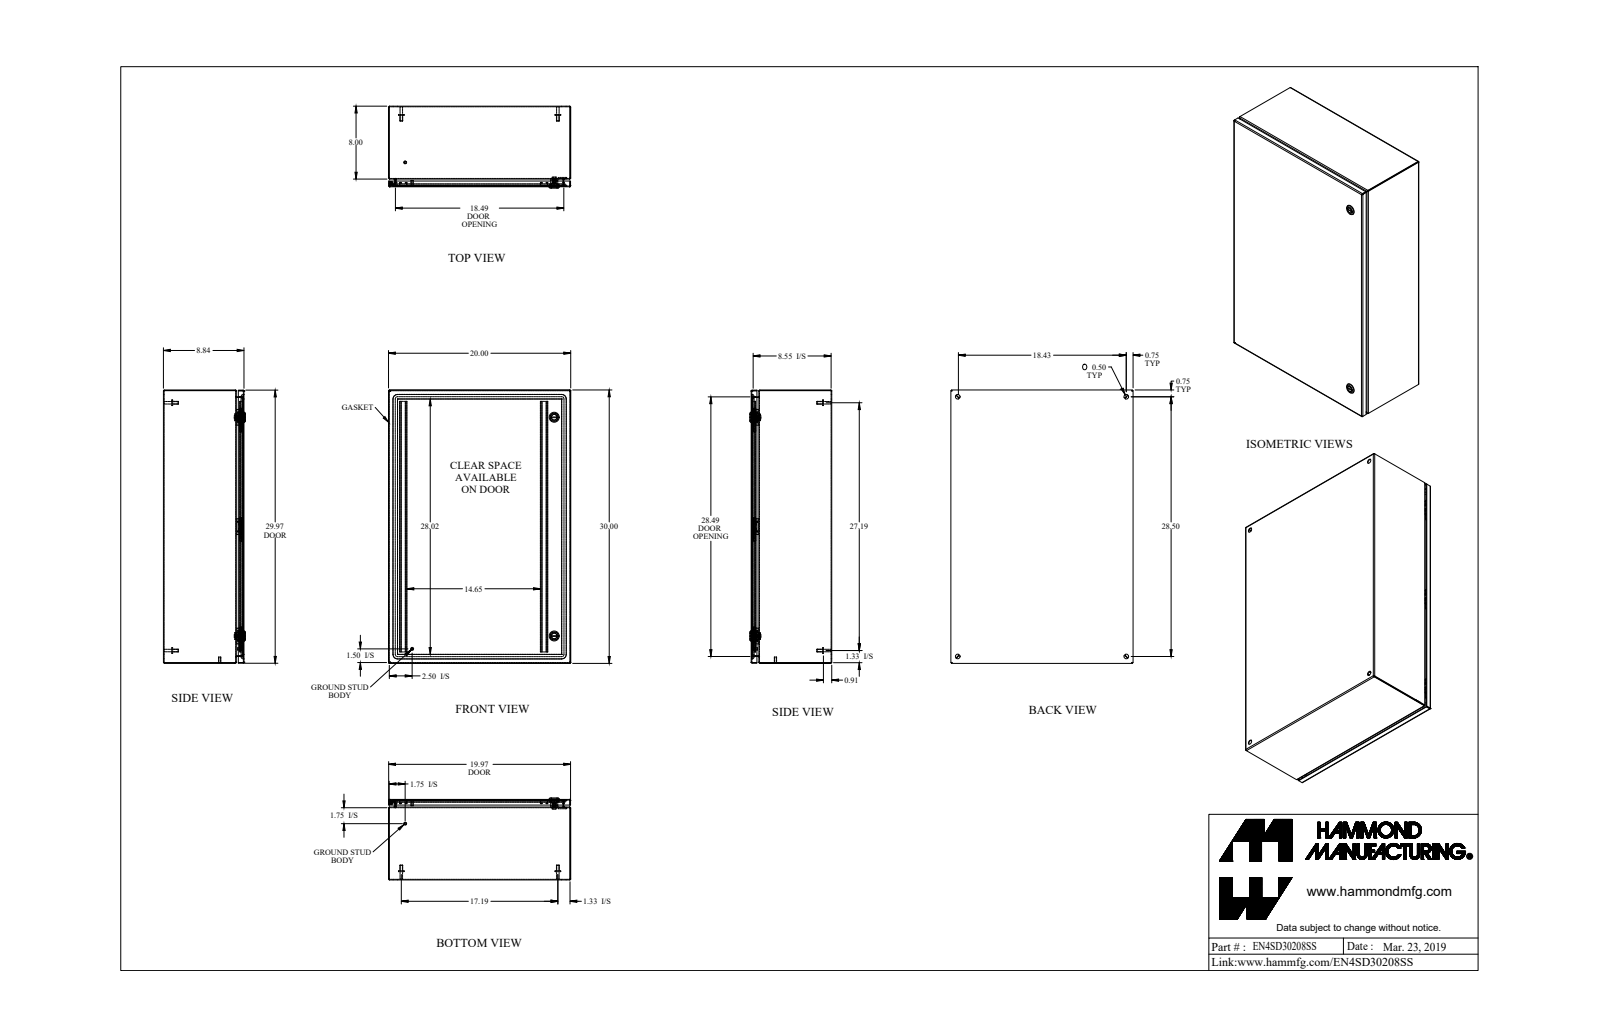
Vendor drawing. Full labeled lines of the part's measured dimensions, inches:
Part name (STEP PRODUCT): EN4SD30208SS_Default
STEP written by: SolidWorks 2019 (CONFIG_CONTROL_DESIGN)
Units: inches
Bodies: 33 solids, 923 faces (450 planar, 301 cylindrical, 172 other)
Overall size (bounding box): 30 × 20 × 9.002
Volume: 171.8 in³ · Surface area: 4 836 in²
Round holes (diameter × count): ⌀0.5 ×6, ⌀0.197 ×2, ⌀0.387 ×2, ⌀0.63 ×2, ⌀0.768 ×2, ⌀0.172 ×1, ⌀0.24 ×1, ⌀0.242 ×1
Round bosses / shafts (diameter × count): ⌀0.625 ×6, ⌀0.313 ×6, ⌀0.275 ×4, ⌀1.1 ×2, ⌀0.785 ×2, ⌀0.525 ×2, ⌀0.25 ×2, ⌀0.236 ×2
Partial cylindrical surfaces — rounded edges, fillets, slot ends (radius × count): R0.036 ×20, R0.108 ×20, R0.25 ×16, R0.01 ×12, R0.048 ×12, R0.006 ×6, R0.062 ×6, R0.125 ×4
Main face-to-face distances: 0.072, 8.77, 8.698, 8.842, 19.928, 29.928, 19.856, 20, 29.856, 30
Hole centre spacings: 2.488, 17.583, 18.5, 26.271, 28.5, 31.515, 33.978, 24
